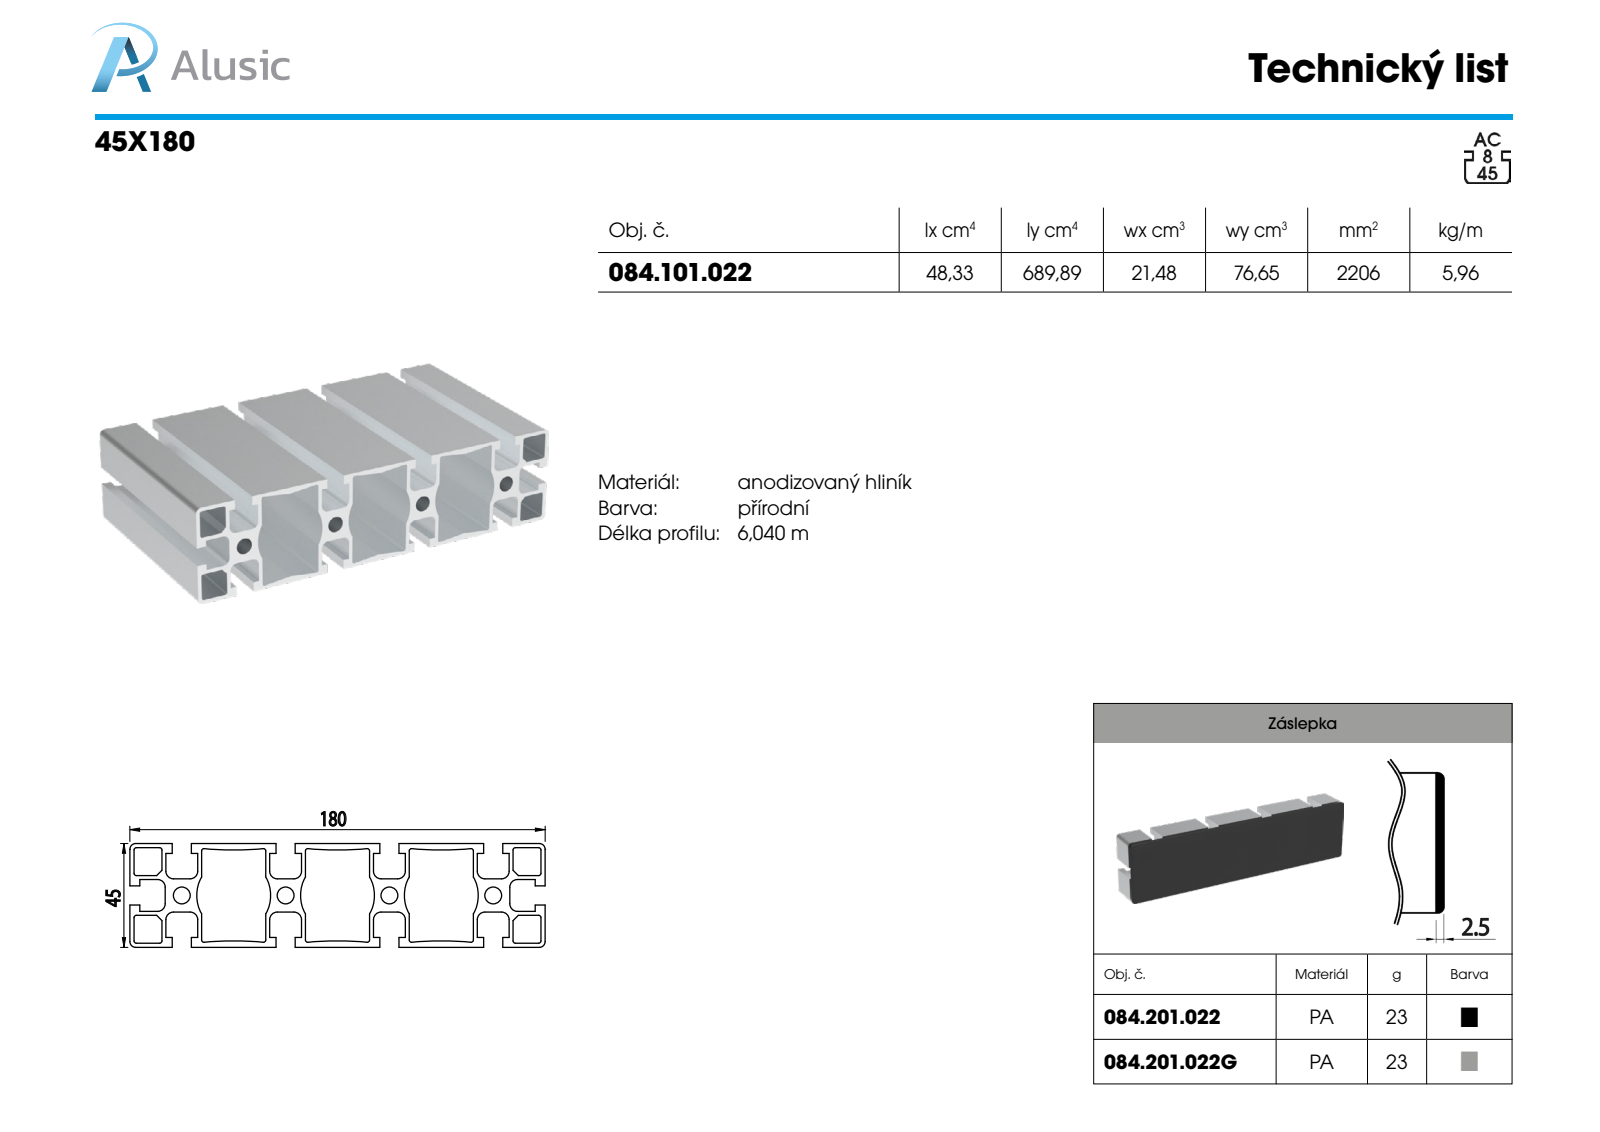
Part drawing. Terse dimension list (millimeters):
name: 084.201.022
written by: SolidWorks 2011 (CONFIG_CONTROL_DESIGN)
unit: mm
bodies: 1 solid, 66 faces (18 planar, 32 cylindrical, 16 other)
size: 180 × 45 × 12.5
volume: 21 427 mm³; area: 19 903 mm²
holes: 4× ⌀9.5, 2× ⌀4.8
bosses: 4× ⌀11.5, 2× ⌀7.5
rounds: 4× R2, 4× R2.5
face distances: 2.5, 45, 12.5, 10, 5, 7.5, 180
hole spacings: 59.91, 104.09, 30, 161, 163.77, 45
